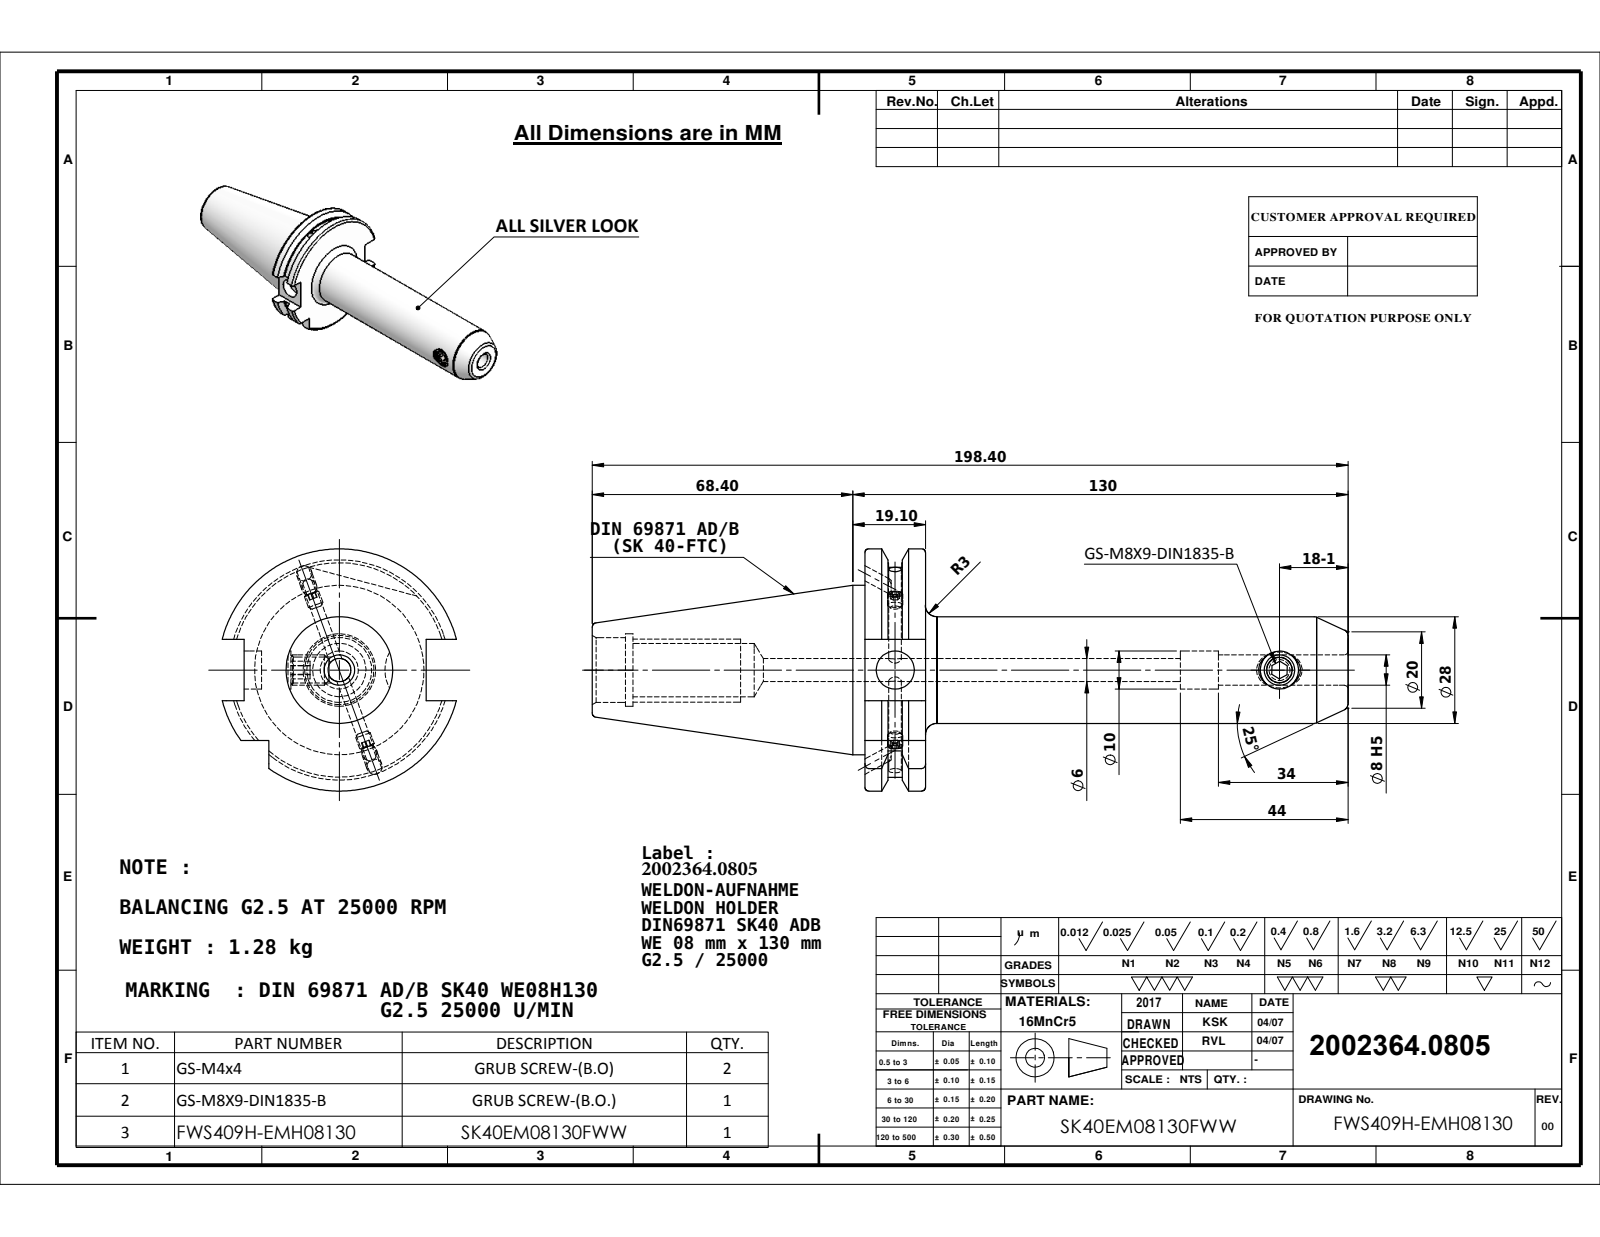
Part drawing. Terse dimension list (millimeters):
name: M8X10._DIN 913 - M8 x 8-N; 91406-WE708130; SK40EM08130FWW; Copy of M4X4_DIN 913 - M4 x 4-N
written by: SolidWorks 2009 (CONFIG_CONTROL_DESIGN)
unit: mm
bodies: 4 solids, 158 faces (58 planar, 44 cylindrical, 56 other)
size: 198.4 × 63.55 × 61.48
volume: 166 438 mm³; area: 32 905 mm²
holes: 3× ⌀10, 1× ⌀3.3, 1× ⌀6, 1× ⌀6.8, 1× ⌀8, 1× ⌀14, 1× ⌀17, 1× ⌀19
bosses: 2× ⌀4, 1× ⌀44.45, 1× ⌀28, 1× ⌀8
rounds: 1× R28.12, 1× R31.77
face distances: 15.9, 126.8, 110.9, 16.1, 47.8, 71.6, 87.5, 198.4, 10.7, 60.9
hole spacings: 100.85
